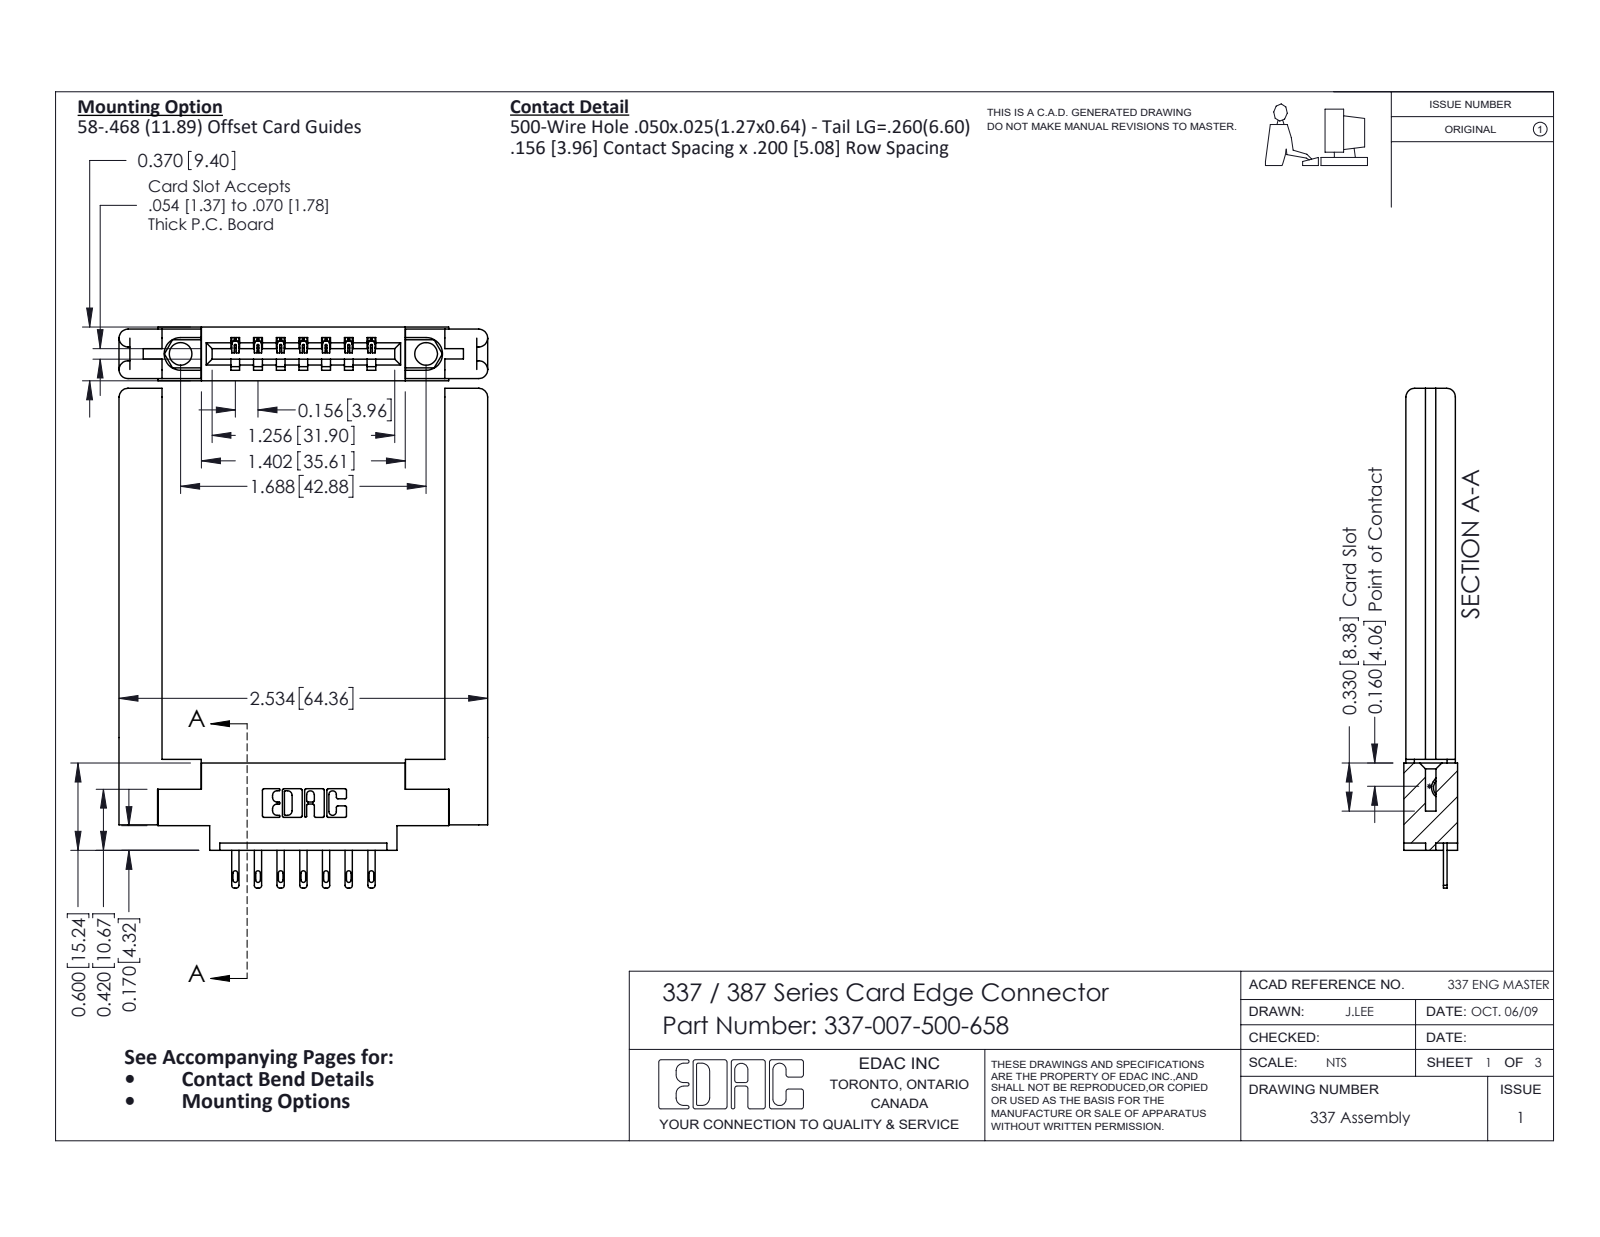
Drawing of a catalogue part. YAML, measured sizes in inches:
part_name: "345-250-001_345-250-001-102; 337 Part_0.170 Offset - 0.156 Dia-TI; 307-220-058; 345-292-001_345-293-100 (+1 more)"
step_written_by: "SolidWorks 2016 (CONFIG_CONTROL_DESIGN)"
units: inches
bodies: {solids: 12, faces: 666, planar: 438, cylindrical: 204, other: 24}
overall_size: [3.435, 2.534, 0.37]
volume: 0.812
surface_area: 17.79
round_holes:
  - {diameter: 0.089, count: 2}
  - {diameter: 0.125, count: 2}
  - {diameter: 0.156, count: 2}
round_bosses_or_shafts:
  - {diameter: 0.155, count: 2}
partial_cylinders:
  - {radius: 0.01, count: 22}
  - {radius: 0.006, count: 14}
  - {radius: 0.016, count: 14}
  - {radius: 0.02, count: 14}
  - {radius: 0.061, count: 8}
  - {radius: 0.007, count: 6}
  - {radius: 0.031, count: 6}
  - {radius: 0.06, count: 5}
face_to_face_distances: [0.355, 0.015, 0.34, 0.15, 0.135, 0.22, 0.206, 0.37, 0.072, 0.148]
hole_center_spacings: [1.688]
